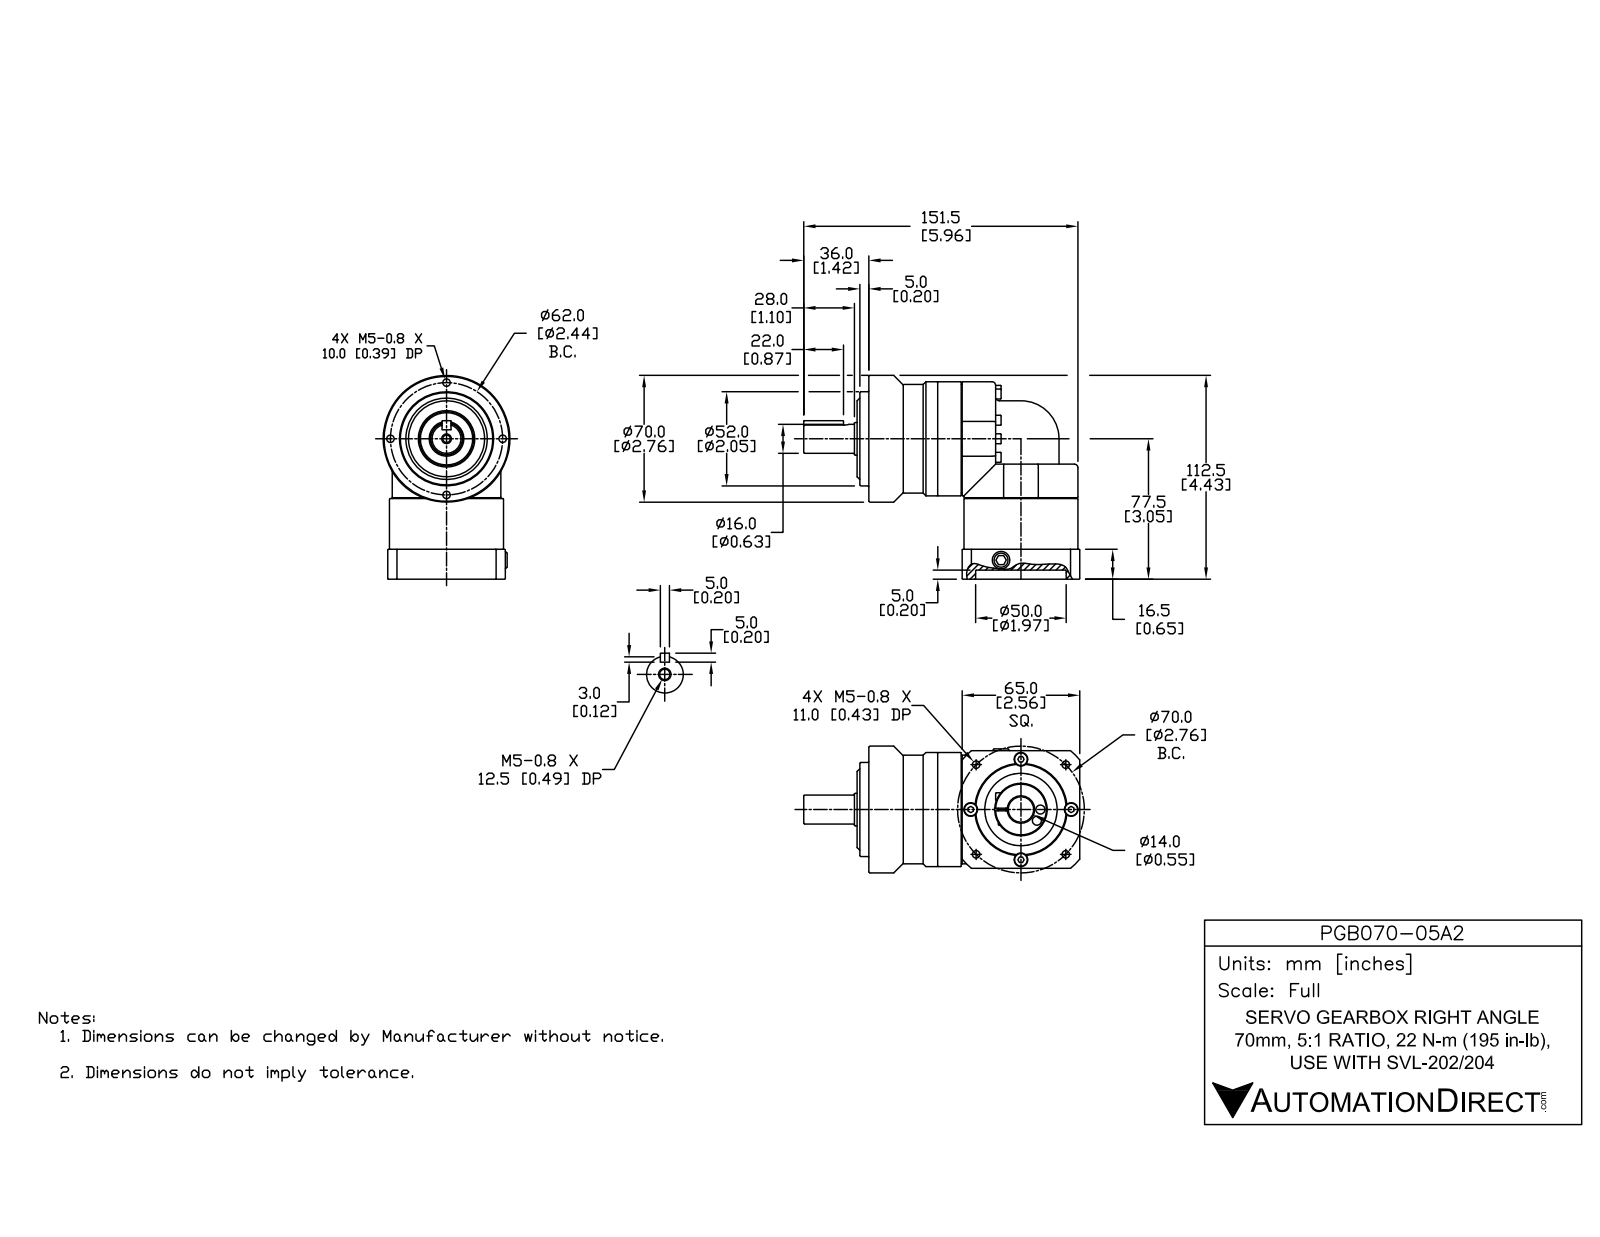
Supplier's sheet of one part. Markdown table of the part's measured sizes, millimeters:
| quantity | value |
| --- | --- |
| part name | PGB070-05A2 |
| STEP written by | SolidWorks 2014 (AUTOMOTIVE_DESIGN) |
| units | millimeters |
| bodies | 1 solid, 499 faces (216 planar, 123 cylindrical, 160 other) |
| overall size | 152.5 × 112.5 × 70 |
| volume | 459 700 mm³ |
| surface area | 54 060 mm² |
| round holes (diameter × count) | 4.1 × 9, 7.5 × 4, 5 × 2, 4.5 × 1, 8 × 1, 14 × 1, 29 × 1, 40 × 1, 50 × 1 |
| round bosses / shafts (diameter × count) | 5.5 × 9, 7 × 5, 63 × 2, 60 × 2, 70 × 1, 52 × 1, 18 × 1, 16 × 1 |
| partial cylindrical surfaces (radius × count) | 2 × 6, 21 × 2, 1.6 × 1, 2.5 × 1, 4 × 1, 42.5 × 1 |
| main face-to-face distances | 65, 16.5, 5, 11.5, 2.5, 62.5, 51.5, 6.5, 58, 1.5 |
| hole center spacings | 24.9, 58, 27.8, 31, 35, 39.2, 43.8, 49.5 |
